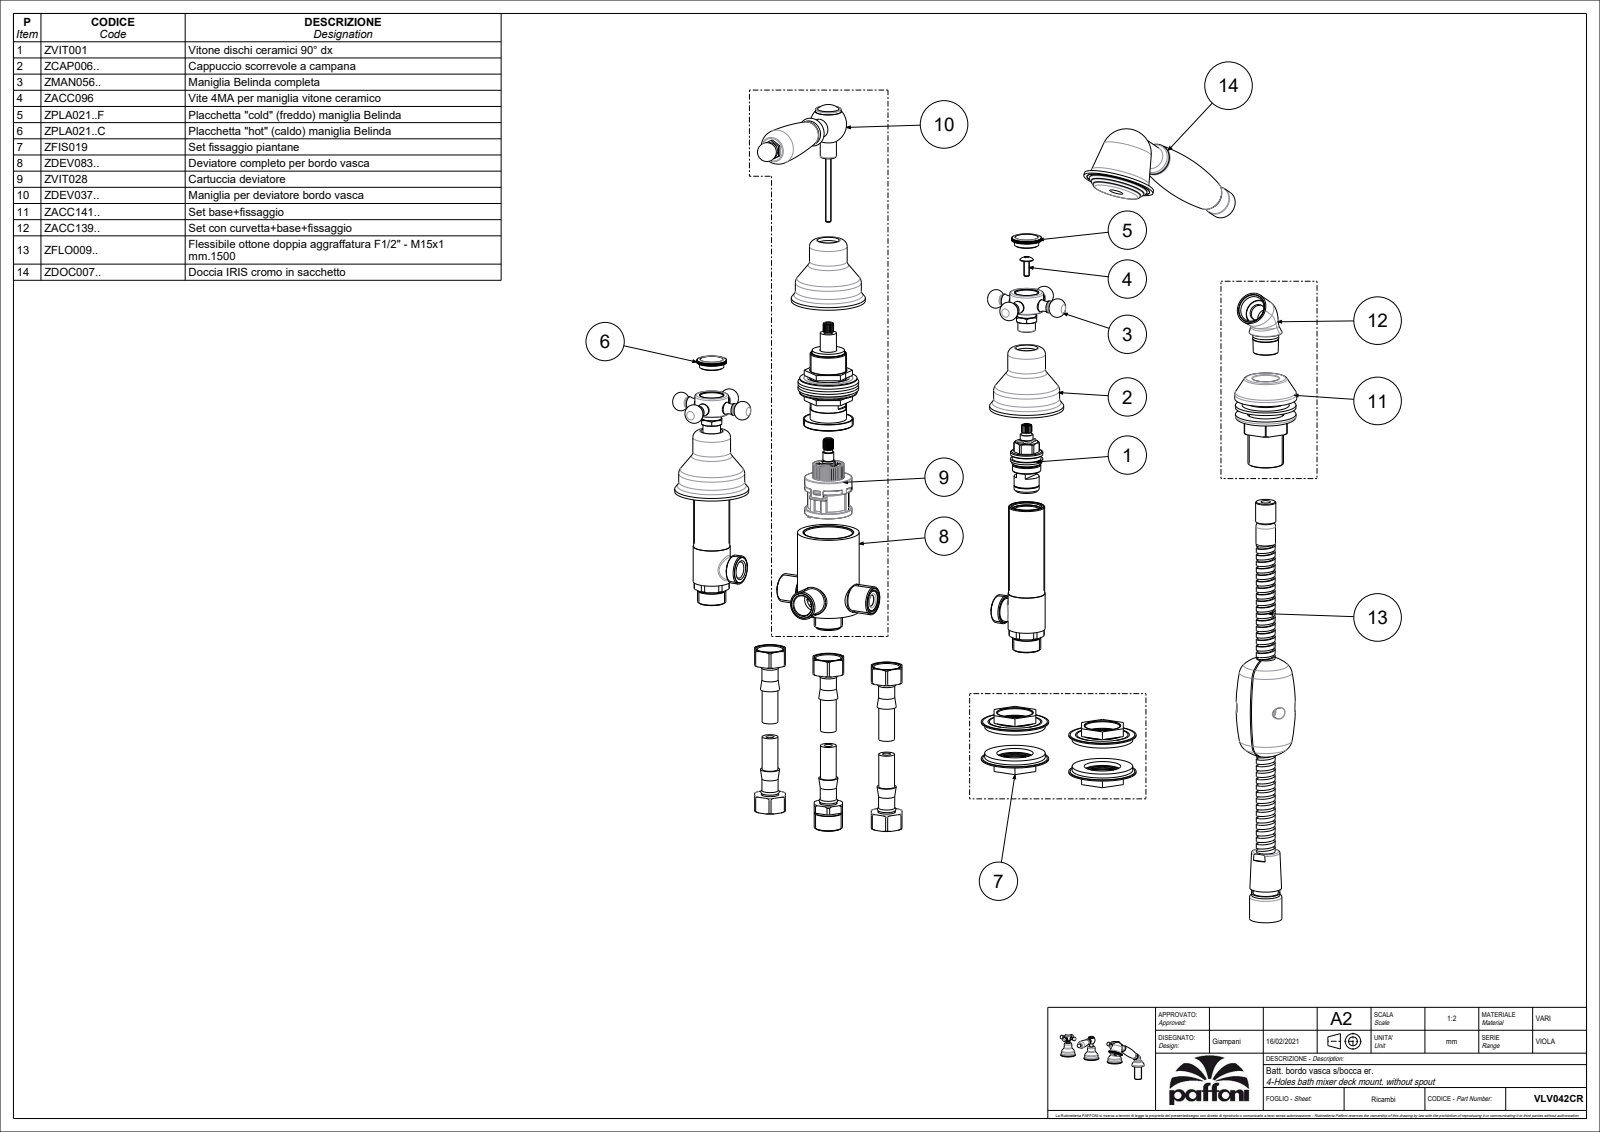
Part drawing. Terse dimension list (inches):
name: VLV042CR
written by: CREO PARAMETRIC BY PTC INC, 2020044 (CONFIG_CONTROL_DESIGN)
unit: in
bodies: 4 solids, 1032 faces (461 planar, 316 cylindrical, 255 other)
size: 14.116 × 8.739 × 4.908
volume: 24.1 in³; area: 123.9 in²
holes: 1× ⌀0.571
bosses: 4× ⌀0.551, 3× ⌀2.165, 3× ⌀1.929, 3× ⌀1.102, 3× ⌀0.354, 3× ⌀0.276, 2× ⌀0.984, 2× ⌀0.512
rounds: 2× R0.433
face distances: 0.236, 2.366, 1.831, 0.535, 0.591, 0.079, 0.618, 1.213, 1.748, 0.157
